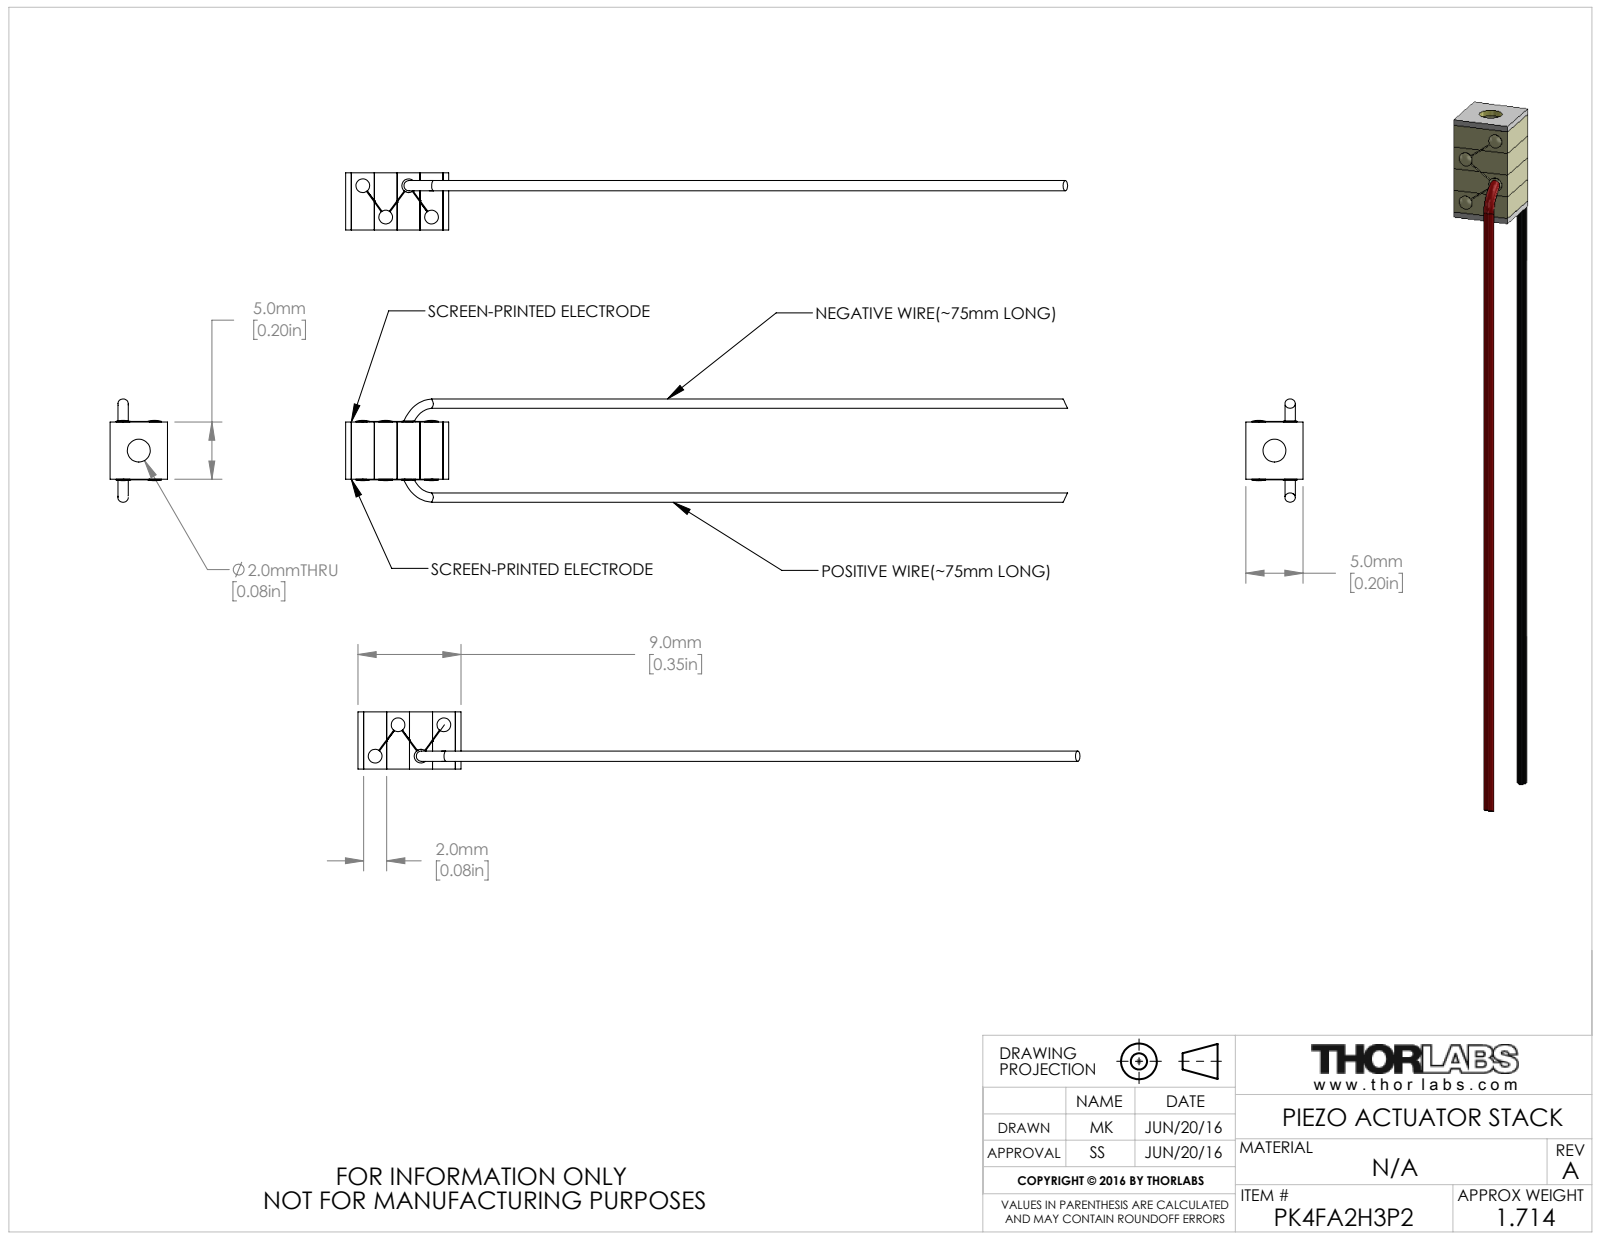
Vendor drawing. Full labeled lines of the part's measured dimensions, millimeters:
Part name (STEP PRODUCT): CTN008938
STEP written by: SolidWorks 2016 (AUTOMOTIVE_DESIGN)
Units: millimetres
Bodies: 3 solids, 132 faces (58 planar, 34 cylindrical, 40 other)
Overall size (bounding box): 63.04 × 9.01 × 5
Volume: 264 mm³ · Surface area: 828 mm²
Round holes (diameter × count): ⌀2 ×1
Round bosses / shafts (diameter × count): ⌀1.2 ×4
Main face-to-face distances: 2, 4, 5, 6, 0.5, 2.5, 4.5, 6.5, 8.5, 8
